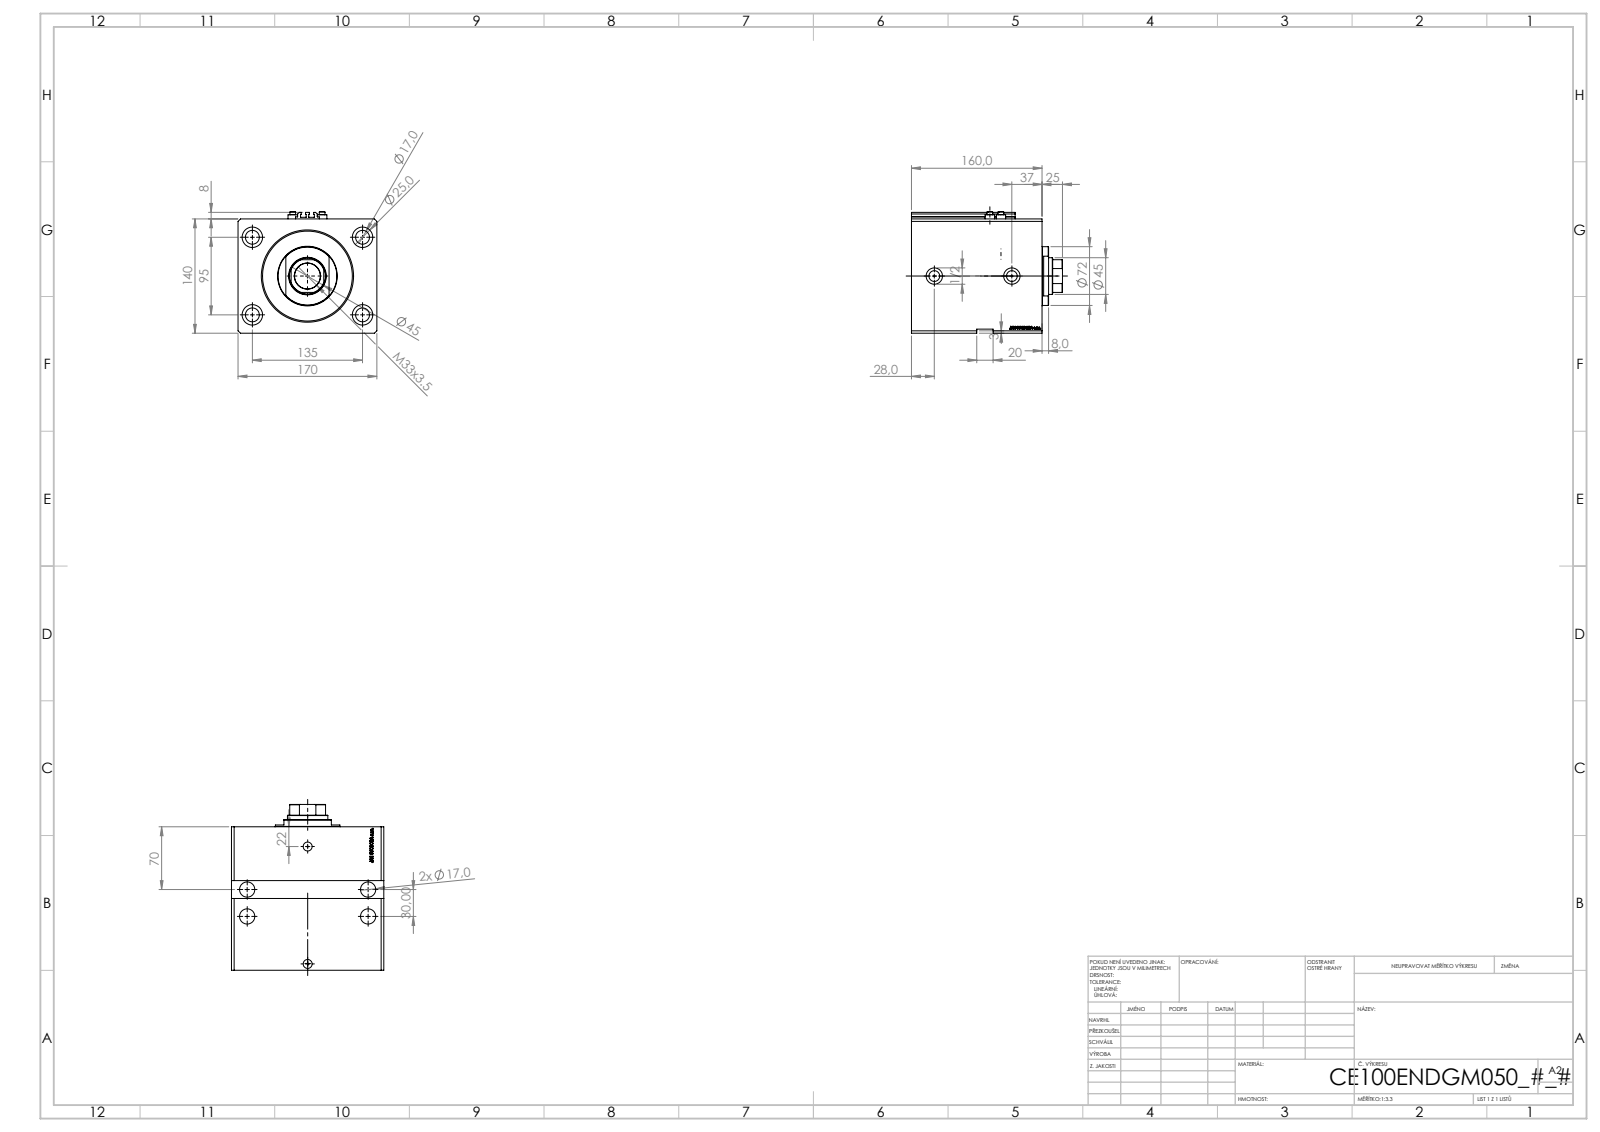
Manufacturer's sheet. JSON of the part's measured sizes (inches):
{"part_name": "ALLEN BOLT V250CE; V250CE_C_VCP; V250CE_E_Body; V250CE_VC_E", "step_written_by": "SolidWorks 2019 (CONFIG_CONTROL_DESIGN)", "units": "inches", "bodies": {"solids": 8, "faces": 1141, "planar": 553, "cylindrical": 150, "other": 438}, "overall_size": [7.283, 6.693, 5.866], "volume_in3": 196.9, "surface_area_in2": 535.1, "round_holes": [[0.669, 8], [0.049, 4], [0.157, 4], [0.984, 4], [0.394, 2], [0.518, 2], [0.787, 2], [1.24, 1], [1.772, 1], [3.937, 1], [4.449, 1]], "round_bosses_or_shafts": [[0.457, 4], [0.276, 4], [2.835, 1]], "partial_cylinders_radius": [[0.008, 10], [0.866, 1]], "face_to_face_distances": [5.512, 6.693, 6.299, 1.138, 5.161, 5.315, 0.984, 4.177, 1.969, 3.346], "hole_center_spacings": [3.25, 5.315, 3.74, 0.535, 1.181, 1.324, 1.417, 1.515]}
